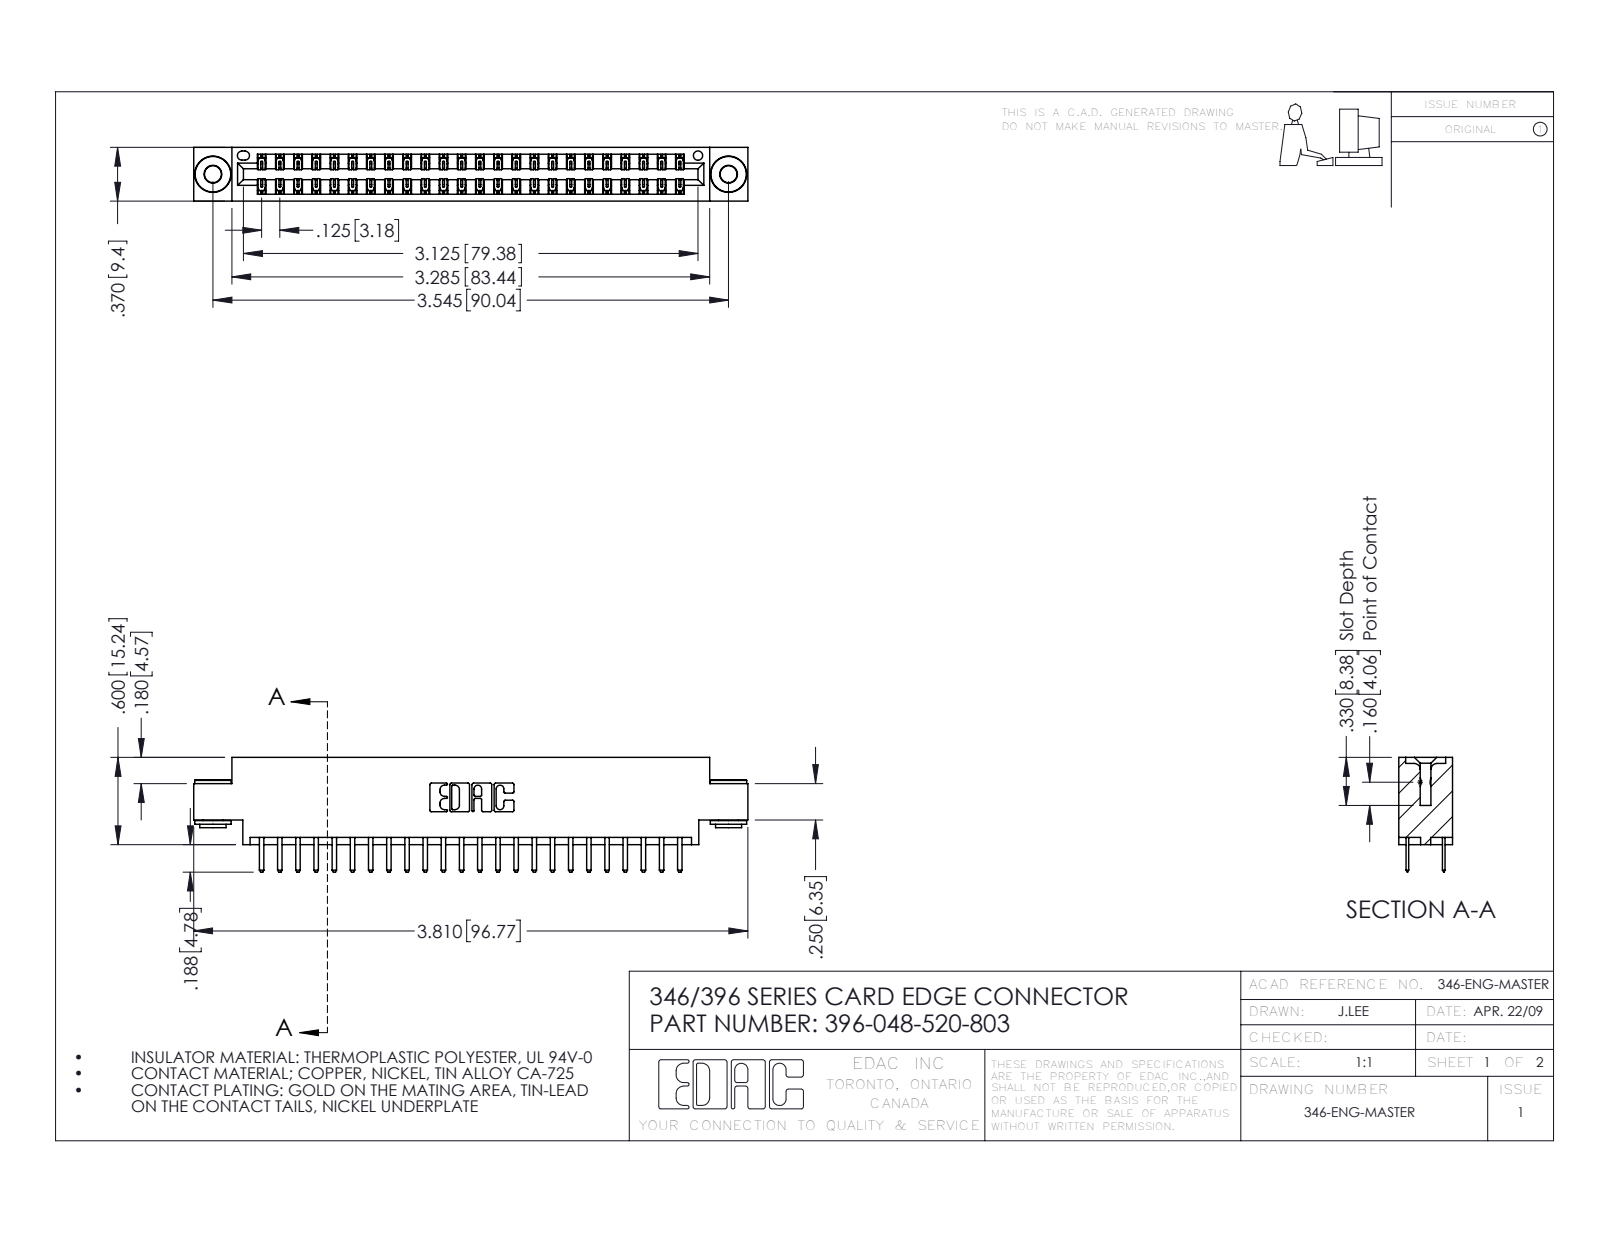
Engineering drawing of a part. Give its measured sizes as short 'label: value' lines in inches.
name: 396-048-520-803; 345-250-002_345-250-002-102; 345-292-001_345-293-120; 346 Part_0.170 Offset - 0.156 Dia-TH
written by: SolidWorks 2016 (CONFIG_CONTROL_DESIGN)
unit: in
bodies: 51 solids, 2852 faces (1866 planar, 978 cylindrical, 8 other)
size: 3.81 × 0.788 × 0.37
volume: 0.558 in³; area: 19.57 in²
holes: 2× ⌀0.116, 2× ⌀0.156, 1× ⌀0.064
bosses: 2× ⌀0.25, 2× ⌀0.18, 2× ⌀0.136
rounds: 72× R0.006, 52× R0.01, 22× R0.01, 6× R0.007, 6× R0.031, 3× R0.026, 2× R0.014, 2× R0.022
face distances: 0.048, 0.322, 0.37, 0.25, 0.025, 0.275, 0.072, 0.298, 0.148, 0.222
hole spacings: 0.246, 3.337, 3.545
